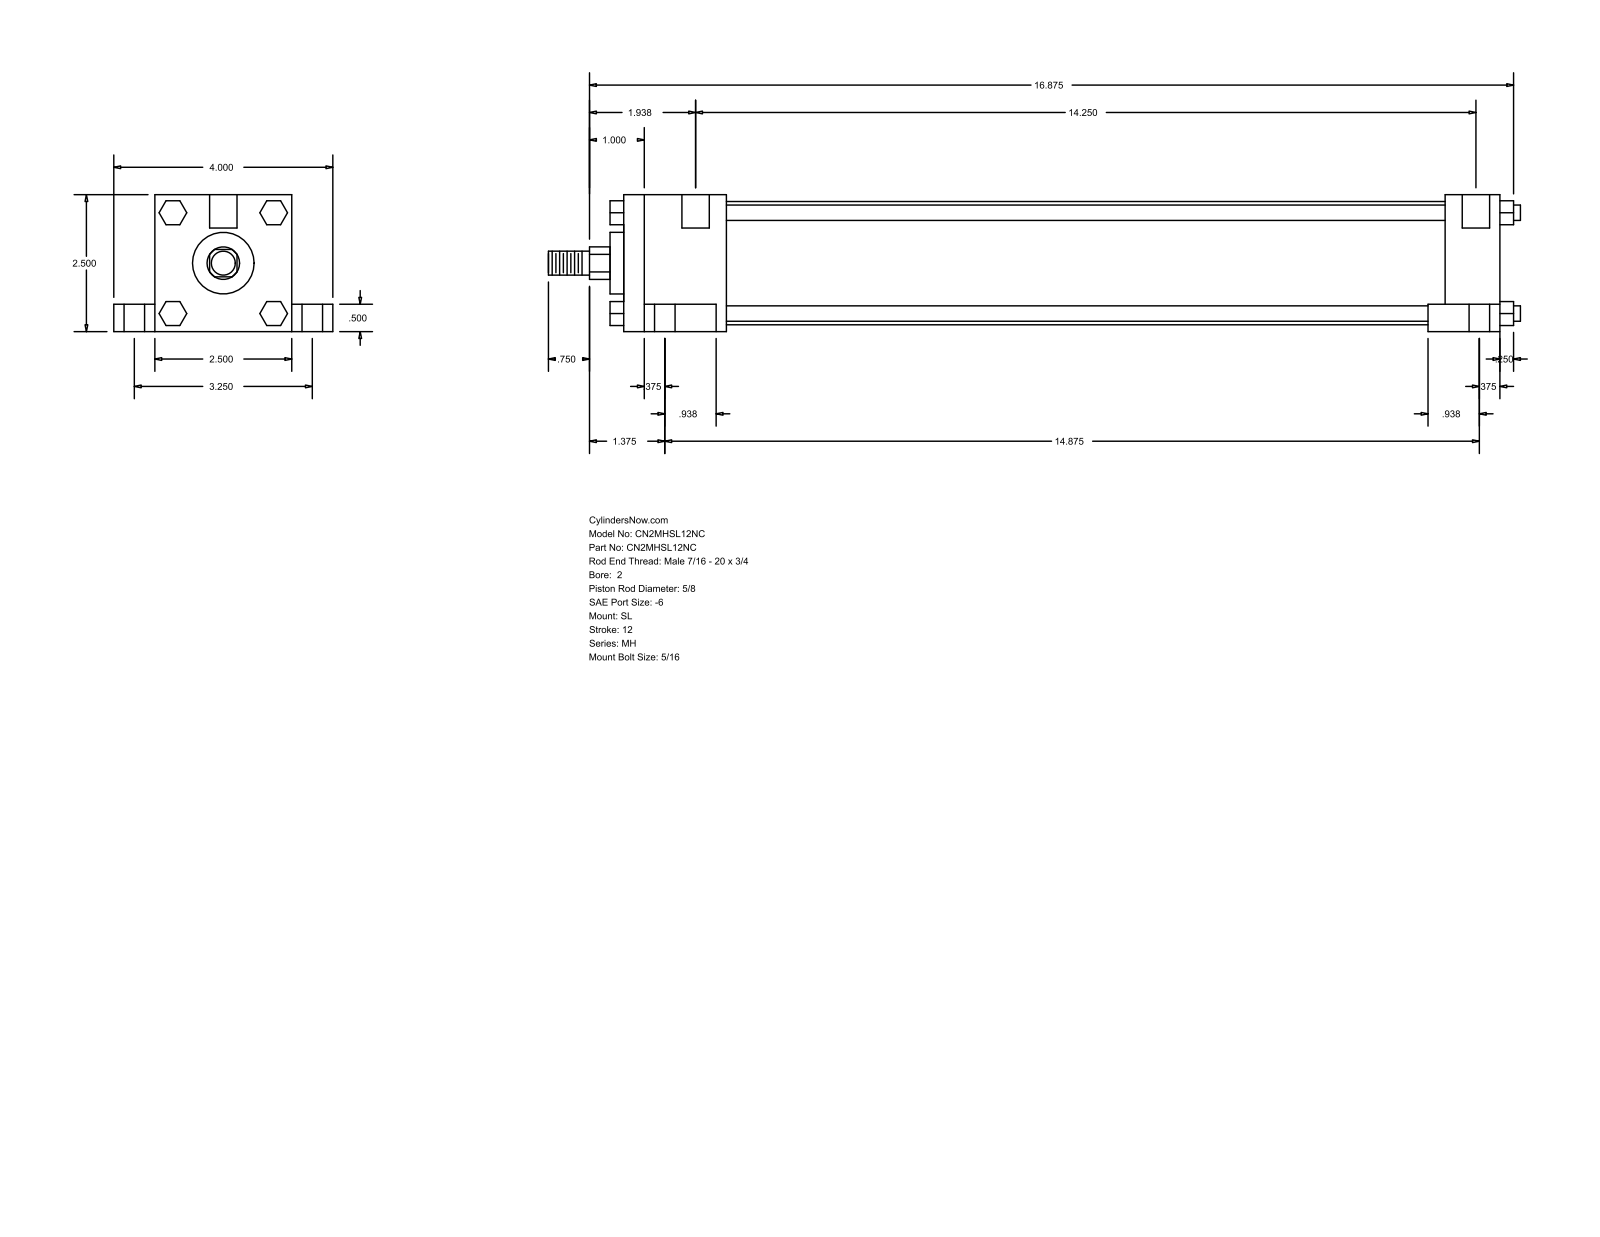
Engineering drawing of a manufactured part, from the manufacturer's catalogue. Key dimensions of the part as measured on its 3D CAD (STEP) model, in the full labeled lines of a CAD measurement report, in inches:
Part name (STEP PRODUCT): MH_SL__0200_0.625
STEP written by: GSSL Pune (CONFIG_CONTROL_DESIGN)
Units: inches
Bodies: 0 solids, 148 faces (112 planar, 36 cylindrical, 0 other)
Overall size (bounding box): 17.75 × 4 × 2.5
Round holes (diameter × count): ⌀0.219 ×4, ⌀0.375 ×4, ⌀0.625 ×4, ⌀0.5 ×2
Round bosses / shafts (diameter × count): ⌀0.281 ×4, ⌀2.25 ×1, ⌀1.125 ×1, ⌀0.625 ×1, ⌀0.437 ×1
Partial cylindrical surfaces — rounded edges, fillets, slot ends (radius × count): R0.297 ×1
Main face-to-face distances: 2.5, 16, 0.5, 0.75, 3.25, 2, 15, 1, 1.875, 13.125
Hole centre spacings: 1.626, 1.668, 1.719, 3.25, 14.405, 14.563, 14.591, 14.875
